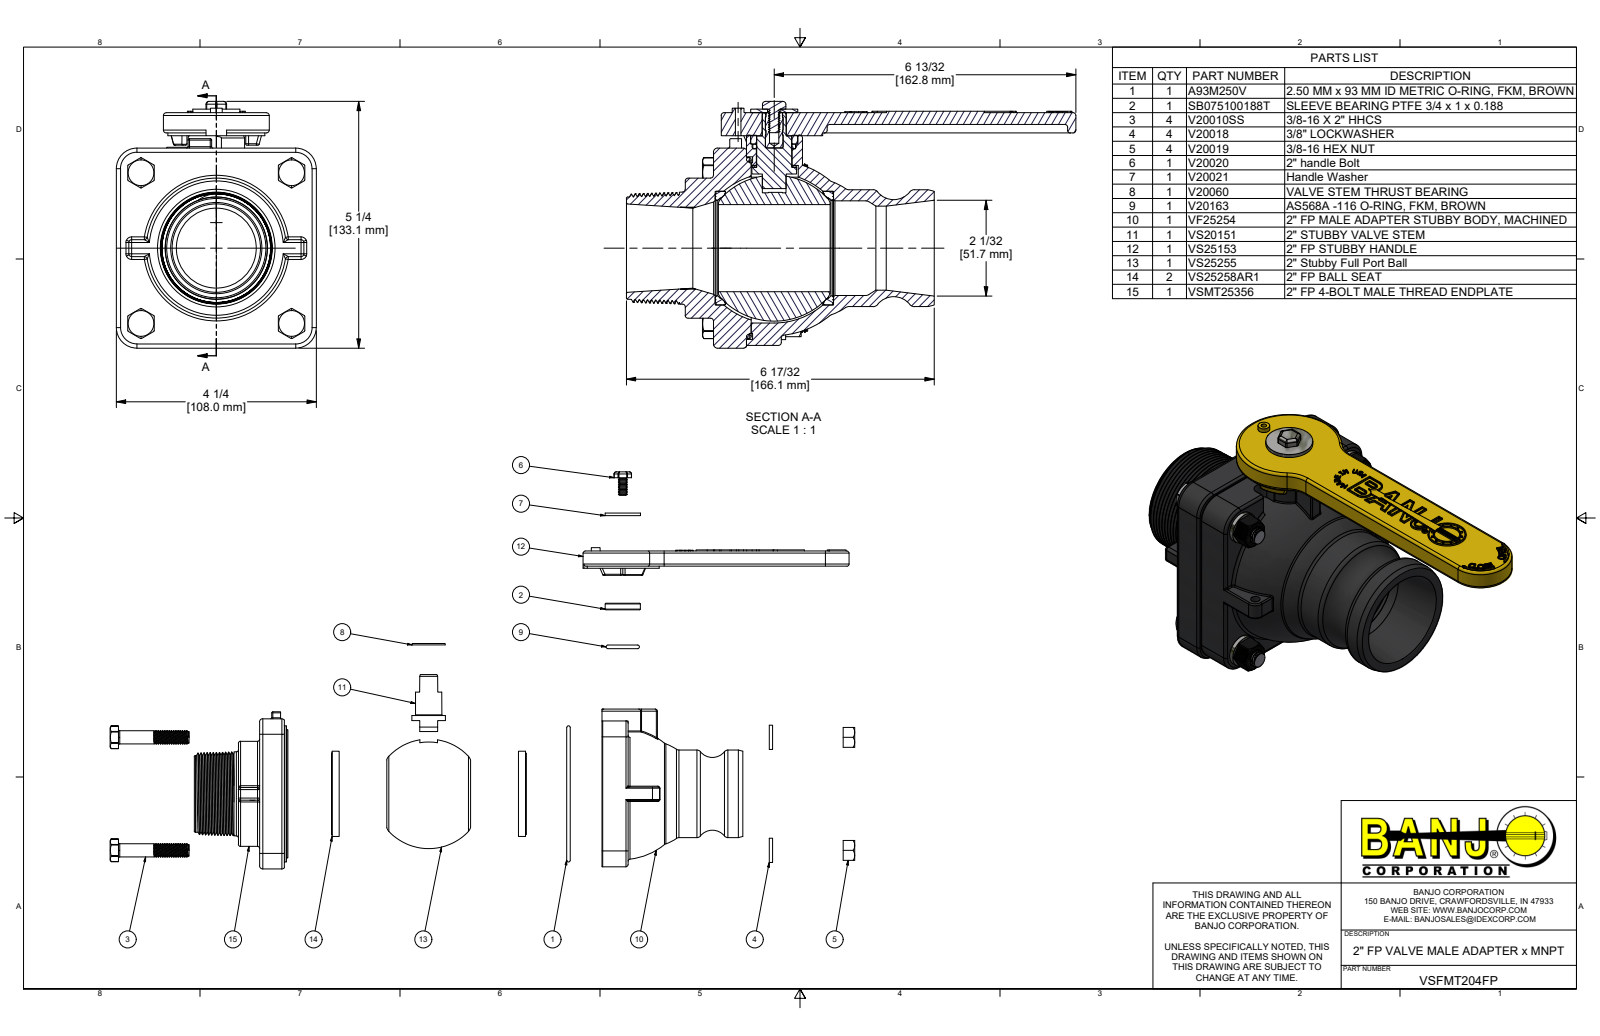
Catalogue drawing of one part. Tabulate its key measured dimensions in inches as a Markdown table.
| quantity | value |
| --- | --- |
| part name | VSFMT204FP; VF25254; VF25254X; VS20151 (+8 more) |
| STEP written by | Autodesk Inventor 2022 (AUTOMOTIVE_DESIGN) |
| units | inches |
| bodies | 26 solids, 1975 faces (626 planar, 600 cylindrical, 749 other) |
| overall size | 9.55 × 5.242 × 4.25 |
| volume | 40.29 in³ |
| surface area | 306.9 in² |
| round holes (diameter × count) | 0.307 × 4, 0.385 × 4, 0.44 × 4, 0.455 × 4, 0.2 × 2, 0.26 × 2, 0.089 × 1, 0.118 × 1, 0.196 × 1, 0.281 × 1, 0.351 × 1, 0.375 × 1 |
| round bosses / shafts (diameter × count) | 0.324 × 60, 0.687 × 4, 0.375 × 4, 3.85 × 1, 3.625 × 1, 2.975 × 1, 2.481 × 1, 2.412 × 1 |
| partial cylindrical surfaces (radius × count) | 0.06 × 47, 0.03 × 30, 0.09 × 8, 0.162 × 8, 0.32 × 4, 0.45 × 4, 0.2 × 3, 0.437 × 3 |
| main face-to-face distances | 0.06, 0.7, 4.19, 0.1, 0.8, 1.44, 0.74, 0.64, 0.25, 4.13 |
| hole center spacings | 2.263, 3.2, 1.79, 2.041, 2.214, 2.341, 2.457, 4.202 |
